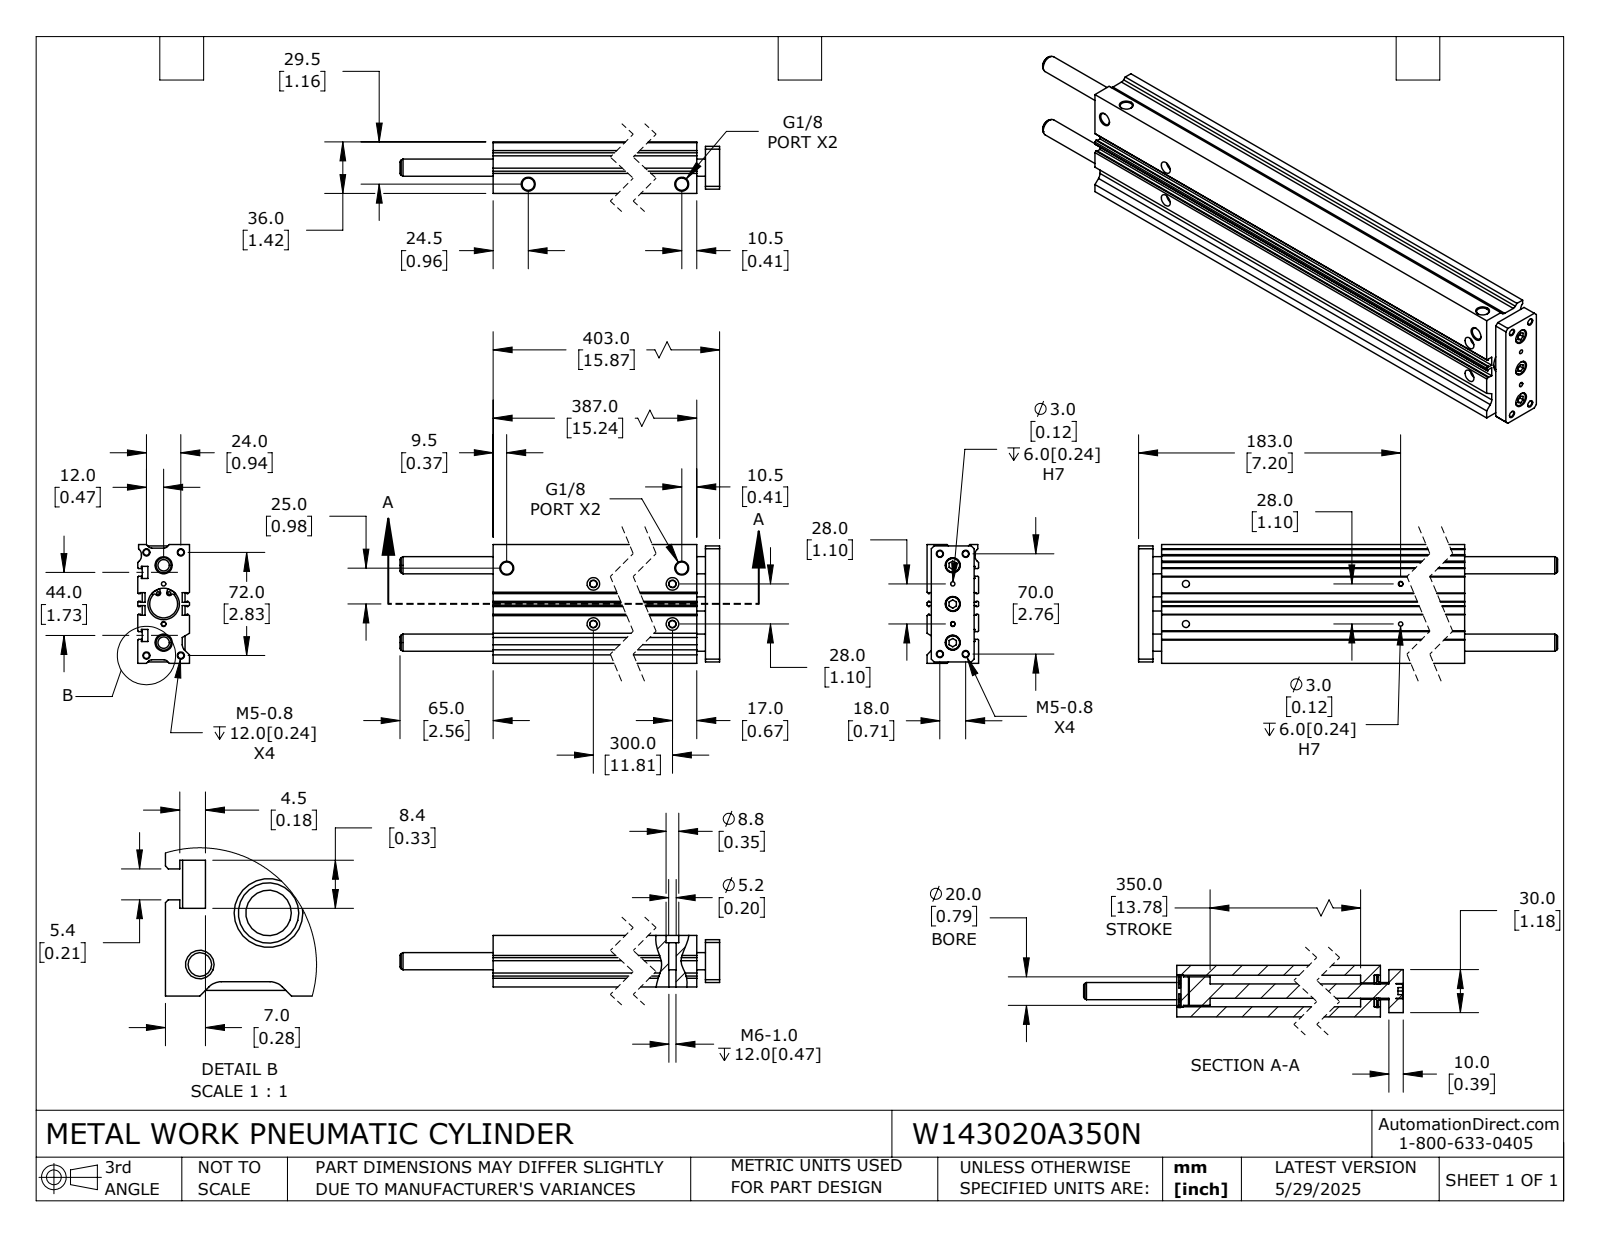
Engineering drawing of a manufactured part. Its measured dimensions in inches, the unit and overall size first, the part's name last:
Units: inches
Overall size (bounding box): 18.425 × 3.268 × 1.417
Round holes (diameter × count): ⌀0.163 ×8, ⌀0.079 ×4, ⌀0.118 ×4, ⌀0.194 ×4, ⌀0.205 ×4, ⌀0.337 ×4, ⌀0.346 ×4, ⌀0.413 ×3, ⌀0.472 ×2, ⌀0.449 ×1, ⌀0.767 ×1, ⌀0.866 ×1
Round bosses / shafts (diameter × count): ⌀0.394 ×3, ⌀0.906 ×2, ⌀0.787 ×1, ⌀0.512 ×1
Partial cylindrical surfaces — rounded edges, fillets, slot ends (radius × count): R0.053 ×4, R0.059 ×4, R0.071 ×4, R0.118 ×4, R0.197 ×3
Main face-to-face distances: 1.417, 0.098, 0.197, 1.22, 0.079, 3.268, 3.169, 0.276, 0.945, 1.142
Hole centre spacings: 0.124, 0.296, 0.336, 0.474, 0.591, 0.78, 0.828, 0.864
Volume: 57.18 in³ · Surface area: 391.2 in²
Bodies: 6 solids, 357 faces (174 planar, 145 cylindrical, 38 other)
Part name (STEP PRODUCT): W143020A350N_ROD; W143020A350N; W143020A350N_BODY
STEP written by: SolidWorks 2024 (CONFIG_CONTROL_DESIGN)
